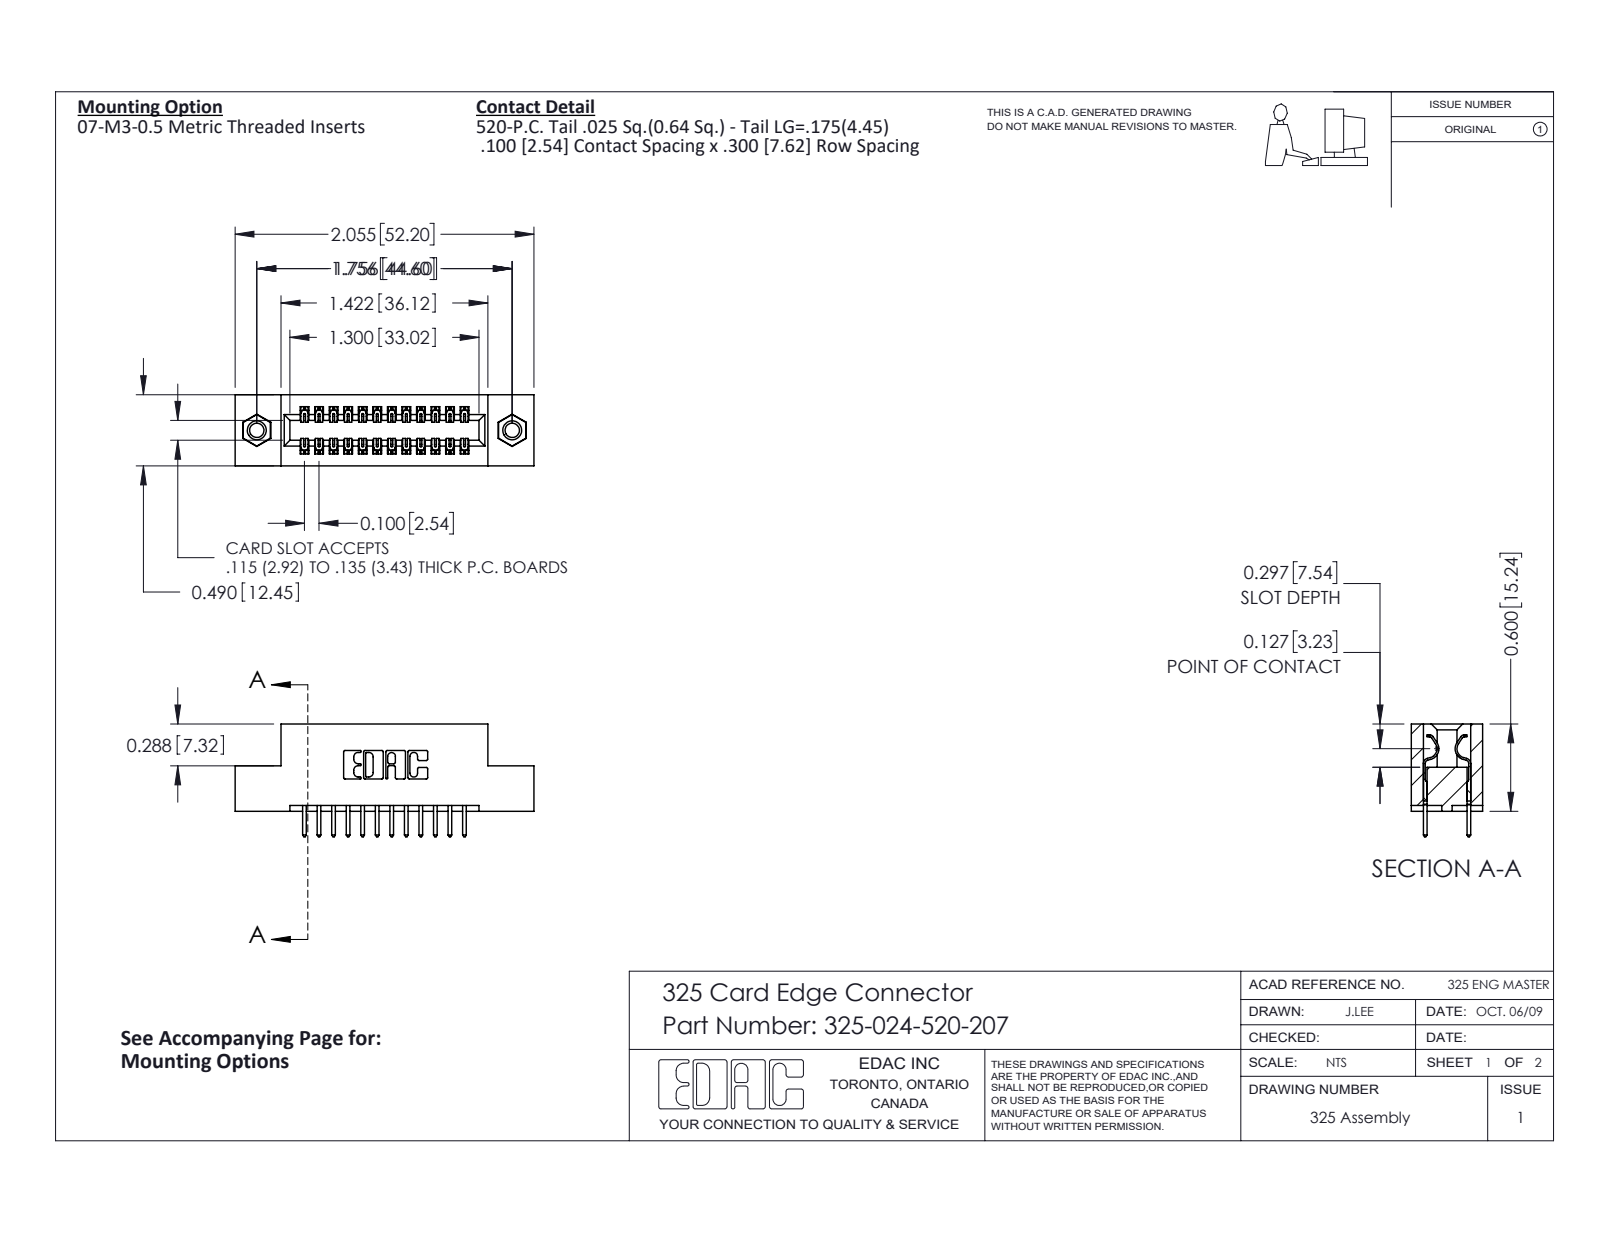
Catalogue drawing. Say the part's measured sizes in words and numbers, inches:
The part is named "345-250-001_345-250-005-103; 325-292-001_325-293-120; 325 Part_TI; 325-024-520-207". Its 3-D file was written by "SolidWorks 2016 (CONFIG_CONTROL_DESIGN)". It is 27 solids with 1422 faces: 966 planar, 440 cylindrical and 16 other. Overall it measures 2.055 by 0.775 by 0.49 inches. Its volume is 0.394 cubic inches and its surface area 10.97 square inches. Round holes: 2 of diameter 0.098, 2 of diameter 0.125, 2 of diameter 0.16. Round bosses or shafts: 2 of diameter 0.155. Partial cylindrical surfaces (rounded edges, fillets, slot ends): 36 of radius 0.006, 24 of radius 0.01, 22 of radius 0.01, 6 of radius 0.007, 6 of radius 0.031, 3 of radius 0.026, 2 of radius 0.014, 2 of radius 0.022. The main face-to-face distances are 0.083, 0.407, 0.3, 0.49, 0.04, 0.1, 0.2, 0.107, 0.383, 0.025. The hole center spacings are 1.756.
